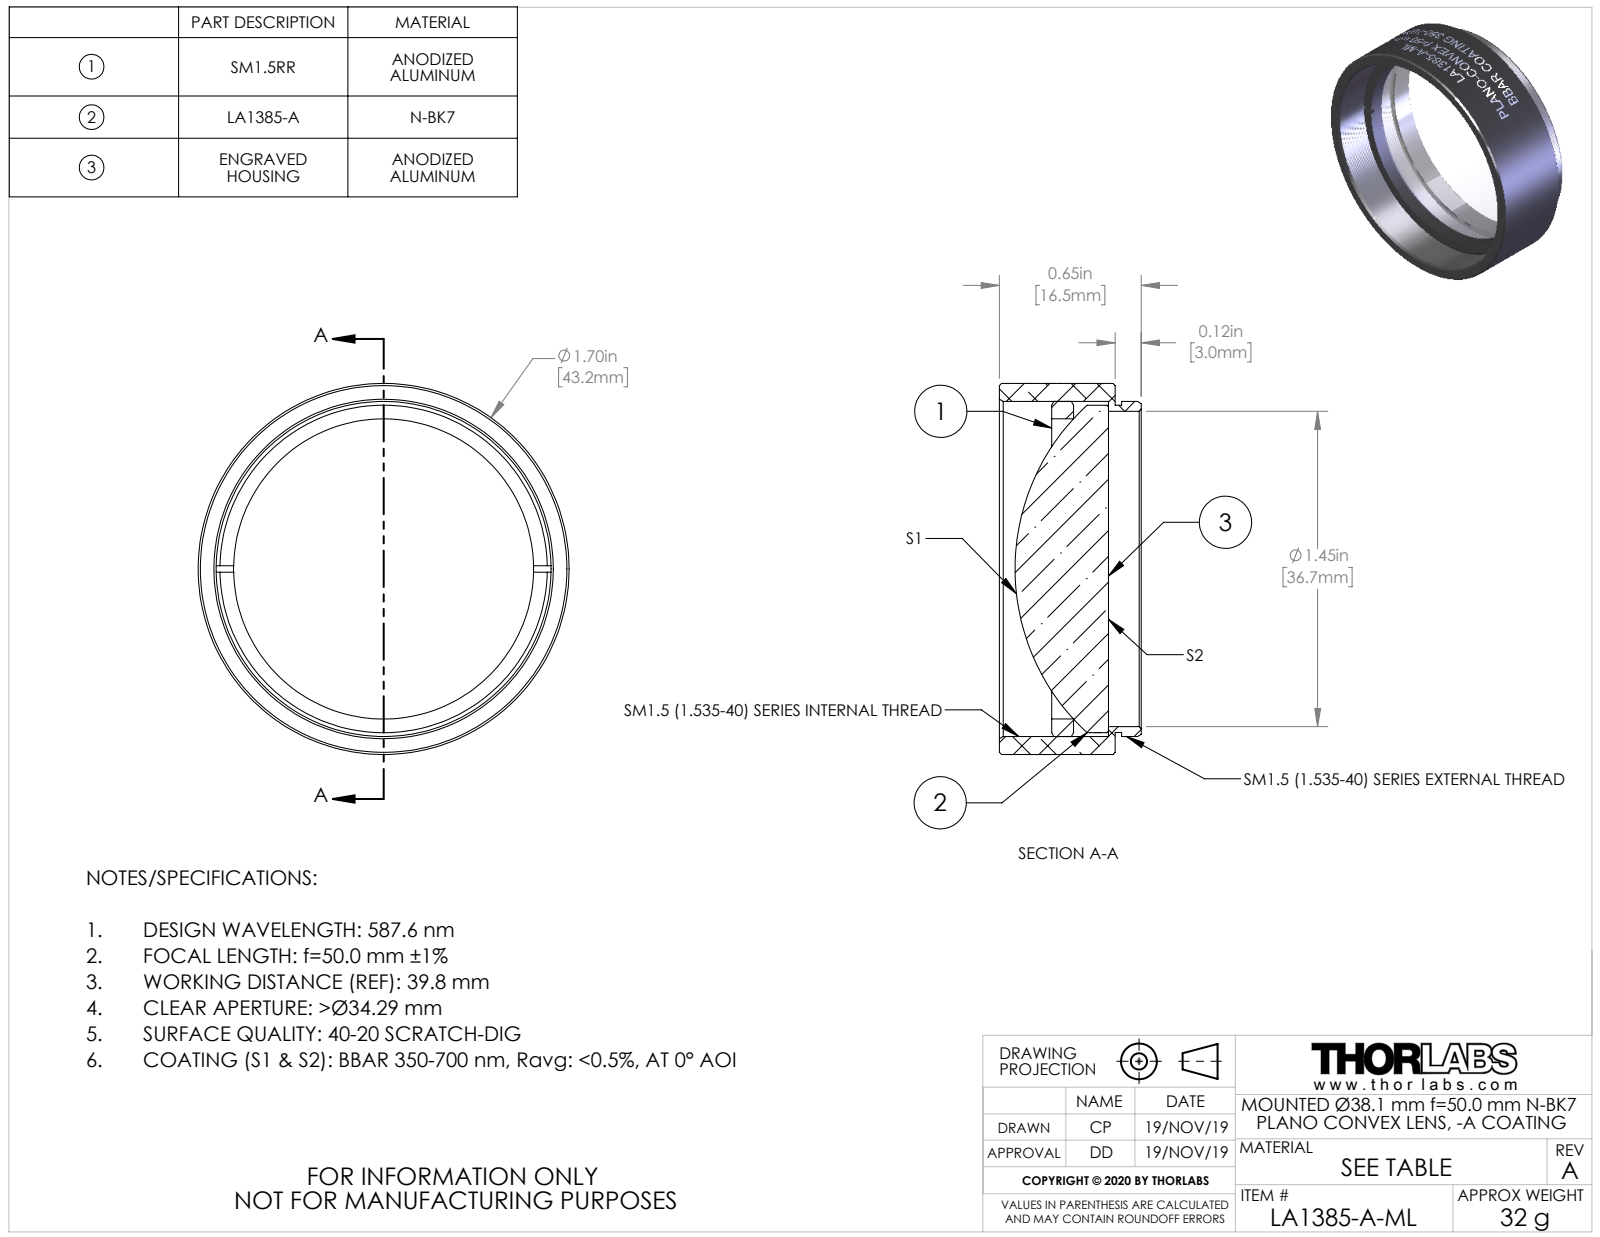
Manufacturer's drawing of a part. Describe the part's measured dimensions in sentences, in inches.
The part is named "TTN200716-E0W". Its 3-D file was written by "SolidWorks 2018 (CONFIG_CONTROL_DESIGN)". It is 3 solids with 155 faces: 15 planar, 121 cylindrical and 19 other. Overall it measures 1.7 by 1.7 by 0.65 inches. Its volume is 0.769 cubic inches and its surface area 13.67 square inches. Round holes: 1 of diameter 1.375, 1 of diameter 1.445, 1 of diameter 1.535. Round bosses or shafts: 1 of diameter 1.7, 1 of diameter 1.535, 1 of diameter 1.5, 1 of diameter 1.499. The main face-to-face distances are 0.03, 0.53, 0.5, 0.191, 0.161, 0.339, 0.291, 0.261, 0.1, 0.239.
